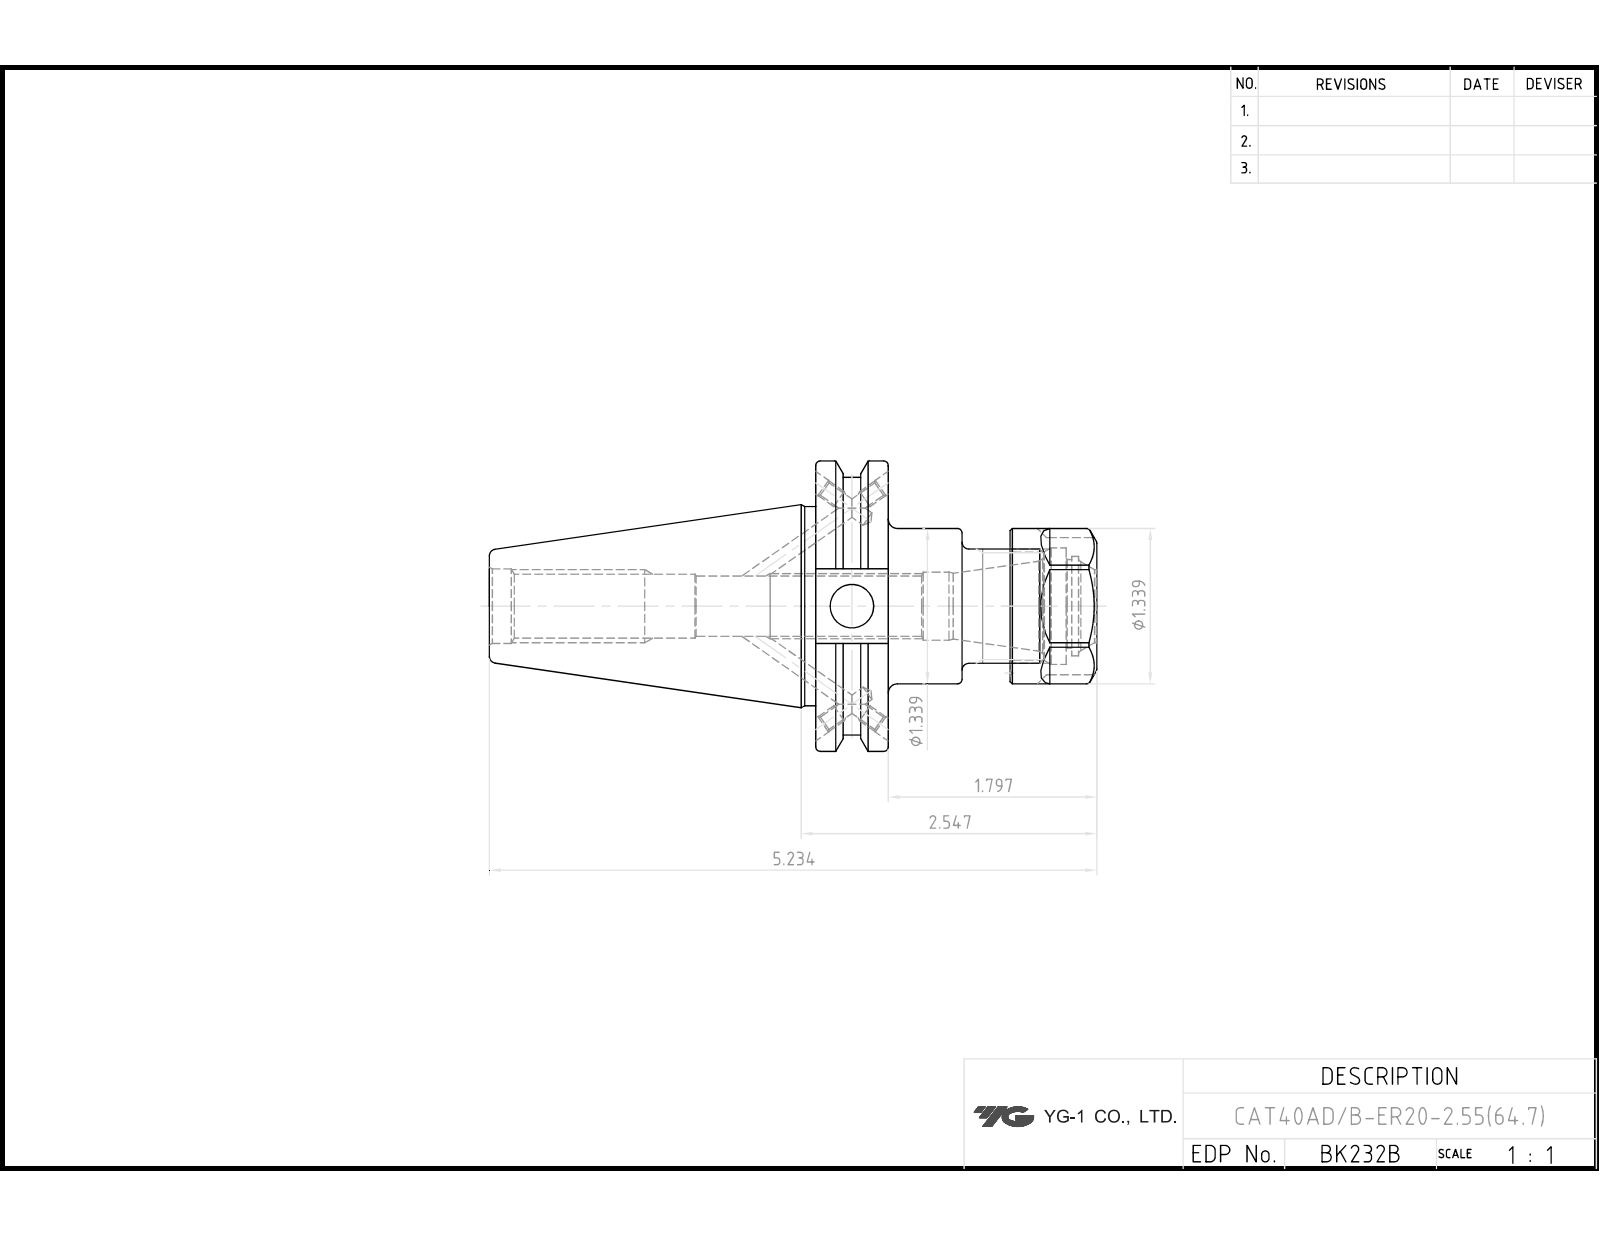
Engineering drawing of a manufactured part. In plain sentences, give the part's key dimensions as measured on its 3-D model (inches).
The part is named "LO-CAT40ADB-ER20-2.55; ER20NUT". Its 3-D file was written by "Autodesk Inventor 2024 (AUTOMOTIVE_DESIGN)". It is 2 solids with 113 faces: 52 planar, 33 cylindrical and 28 other. Overall it measures 5.234 by 2.5 by 2.405 inches. Its volume is 7.682 cubic inches and its surface area 47.74 square inches. Round holes: 4 of diameter 0.128, 4 of diameter 0.157, 1 of diameter 0.375, 1 of diameter 0.495, 1 of diameter 0.527, 1 of diameter 0.587, 1 of diameter 0.63, 1 of diameter 0.642, 1 of diameter 0.724, 1 of diameter 0.857, 1 of diameter 0.925, 1 of diameter 1.004. Round bosses or shafts: 1 of diameter 2.5, 1 of diameter 2.217, 1 of diameter 1.717, 1 of diameter 1.339, 1 of diameter 0.984. The main face-to-face distances are 0.625, 1.181, 2.422, 1.797, 0.748, 1.674, 1.049, 2.159, 1.533, 0.484. The hole center spacings are 1.383.
